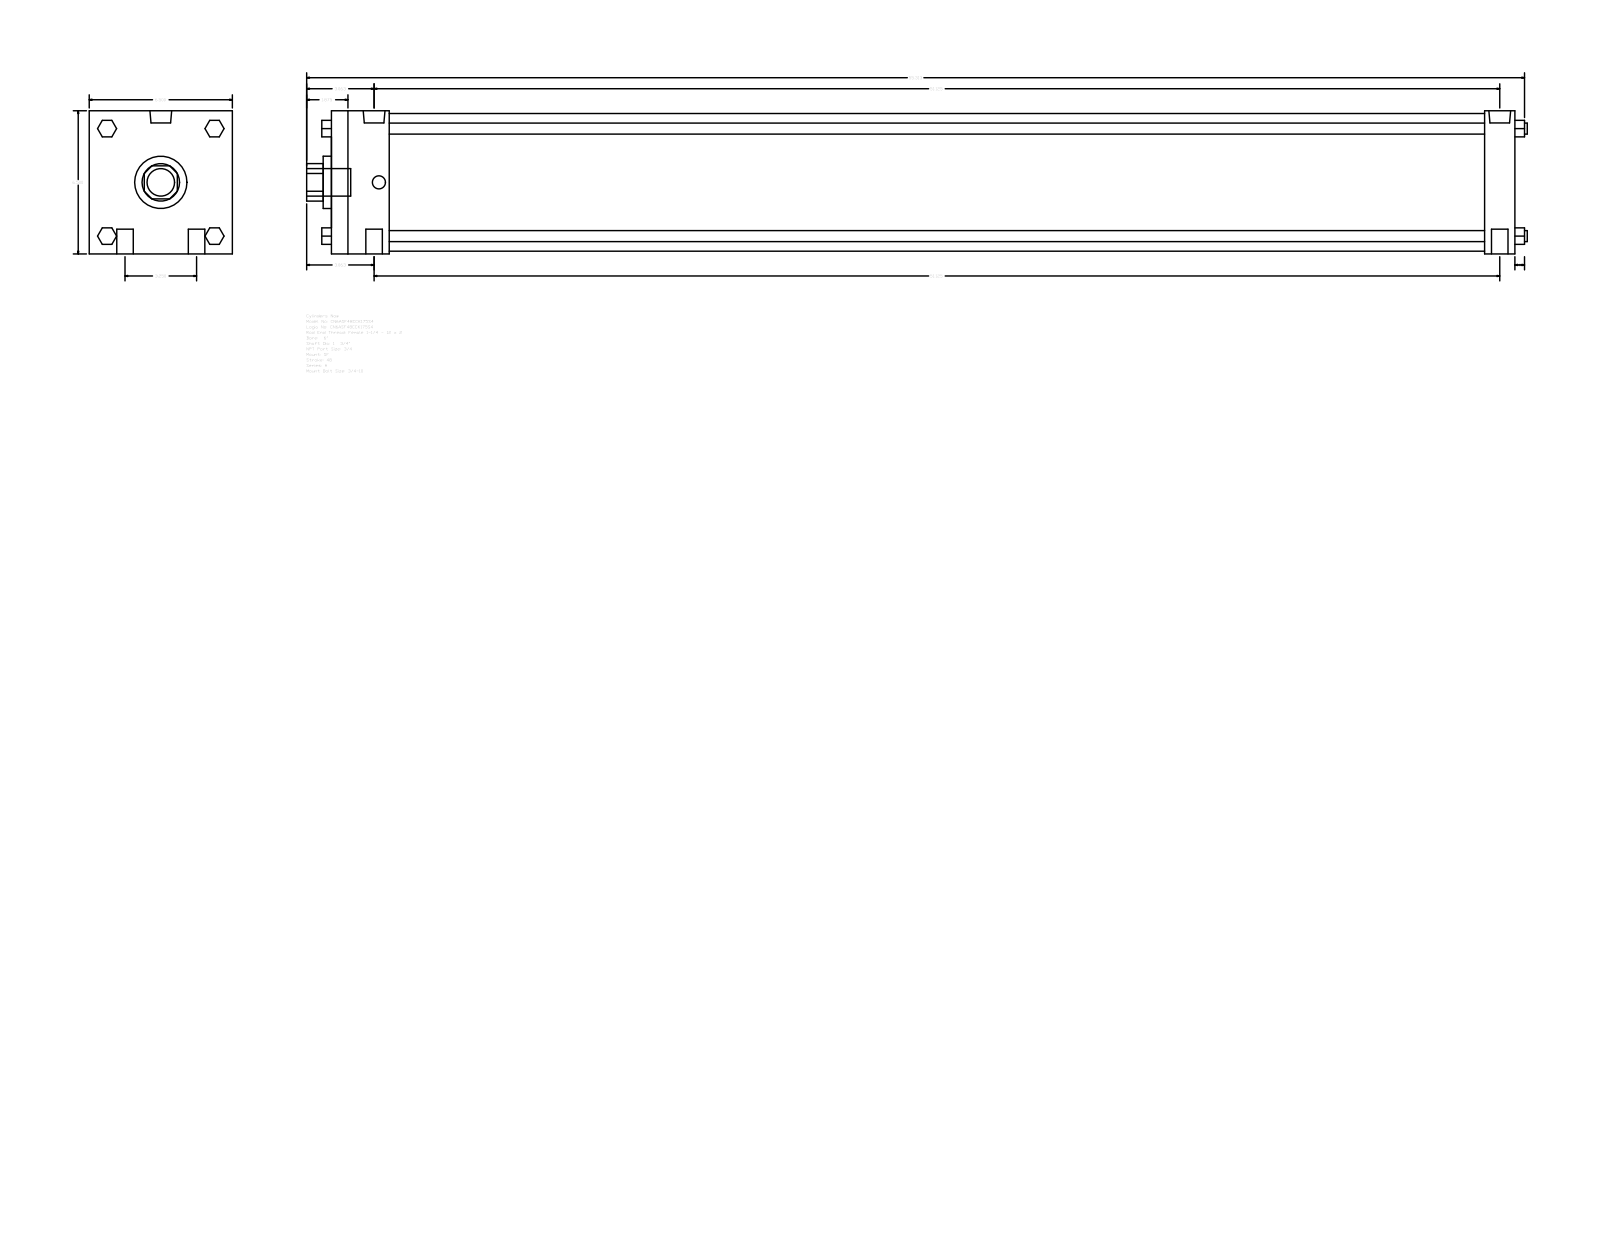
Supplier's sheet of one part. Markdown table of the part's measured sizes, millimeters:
| quantity | value |
| --- | --- |
| part name | A_SF__0600_1.75 |
| STEP written by | GSSL Pune (CONFIG_CONTROL_DESIGN) |
| units | millimeters |
| bodies | 0 solids, 124 faces (94 planar, 30 cylindrical, 0 other) |
| overall size | 1408.11 × 165.1 × 165.1 |
| round holes (diameter × count) | 44.45 × 1, 60.33 × 1, 158.75 × 1 |
| round bosses / shafts (diameter × count) | 19.05 × 4, 12.7 × 4, 25.12 × 2, 15.08 × 2, 31.75 × 1 |
| partial cylindrical surfaces (radius × count) | 21.63 × 1 |
| main face-to-face distances | 165.1, 1365.26, 1330.33, 34.93, 66.68, 1263.65, 1298.58, 19.05, 61.97, 107.34 |
